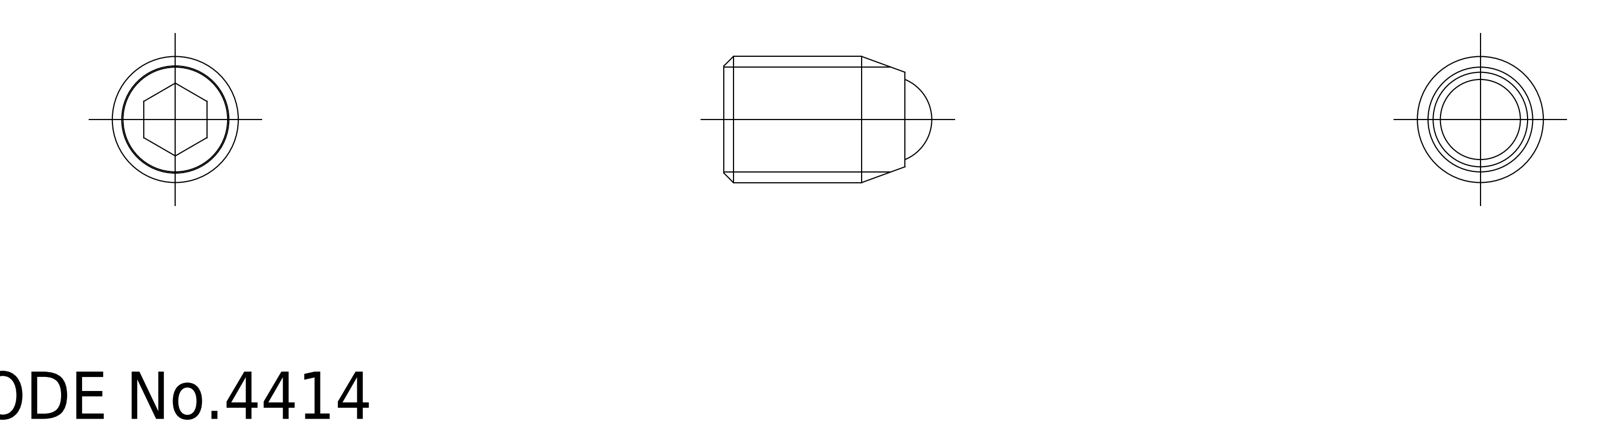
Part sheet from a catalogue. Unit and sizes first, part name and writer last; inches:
Units: inches
Overall size (bounding box): 0.52 × 0.315 × 0.315
Volume: 0.027 in³ · Surface area: 0.947 in²
Bodies: 2 solids, 20 faces (0 planar, 0 cylindrical, 20 other)
Part name (STEP PRODUCT): ball; SCSS_M8_12_R_19236_36
STEP written by: CADfix (AUTOMOTIVE_DESIGN)
